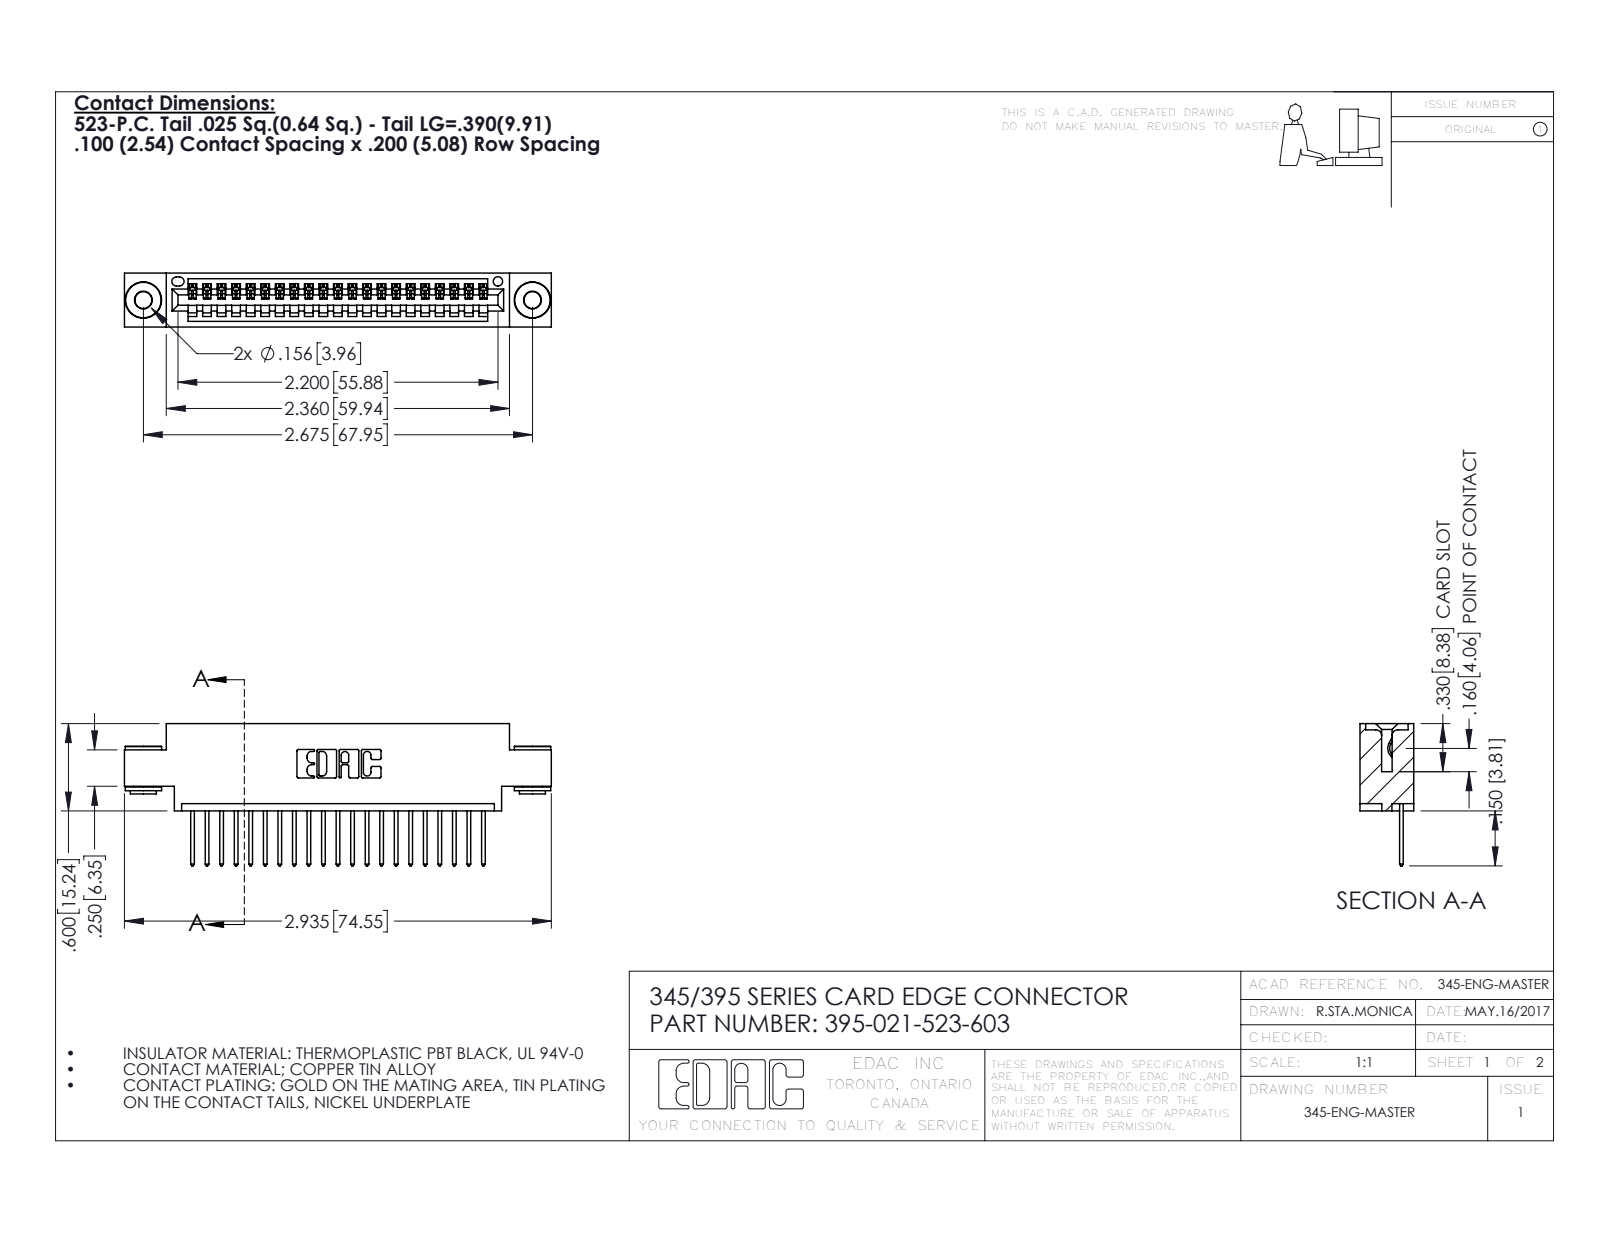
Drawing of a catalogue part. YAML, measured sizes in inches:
part_name: "345-292-001_345-293-123; 395-021-523-603; 345 Part_0.170 Offset - 0.156 Dia-TH; 345-250-002_345-250-002-102"
step_written_by: "SolidWorks 2016 (CONFIG_CONTROL_DESIGN)"
units: inches
bodies: {solids: 24, faces: 1386, planar: 934, cylindrical: 444, other: 8}
overall_size: [2.935, 0.977, 0.37]
volume: 0.415
surface_area: 14.14
round_holes:
  - {diameter: 0.116, count: 2}
  - {diameter: 0.156, count: 2}
  - {diameter: 0.064, count: 1}
round_bosses_or_shafts:
  - {diameter: 0.25, count: 2}
  - {diameter: 0.18, count: 2}
  - {diameter: 0.136, count: 2}
partial_cylinders:
  - {radius: 0.006, count: 42}
  - {radius: 0.01, count: 42}
  - {radius: 0.01, count: 22}
  - {radius: 0.007, count: 6}
  - {radius: 0.031, count: 6}
  - {radius: 0.026, count: 3}
  - {radius: 0.031, count: 2}
  - {radius: 0.04, count: 2}
face_to_face_distances: [0.072, 0.298, 0.37, 0.2, 0.098, 0.272, 0.025, 0.225, 0.175, 0.1]
hole_center_spacings: [0.27, 2.441, 2.675]
